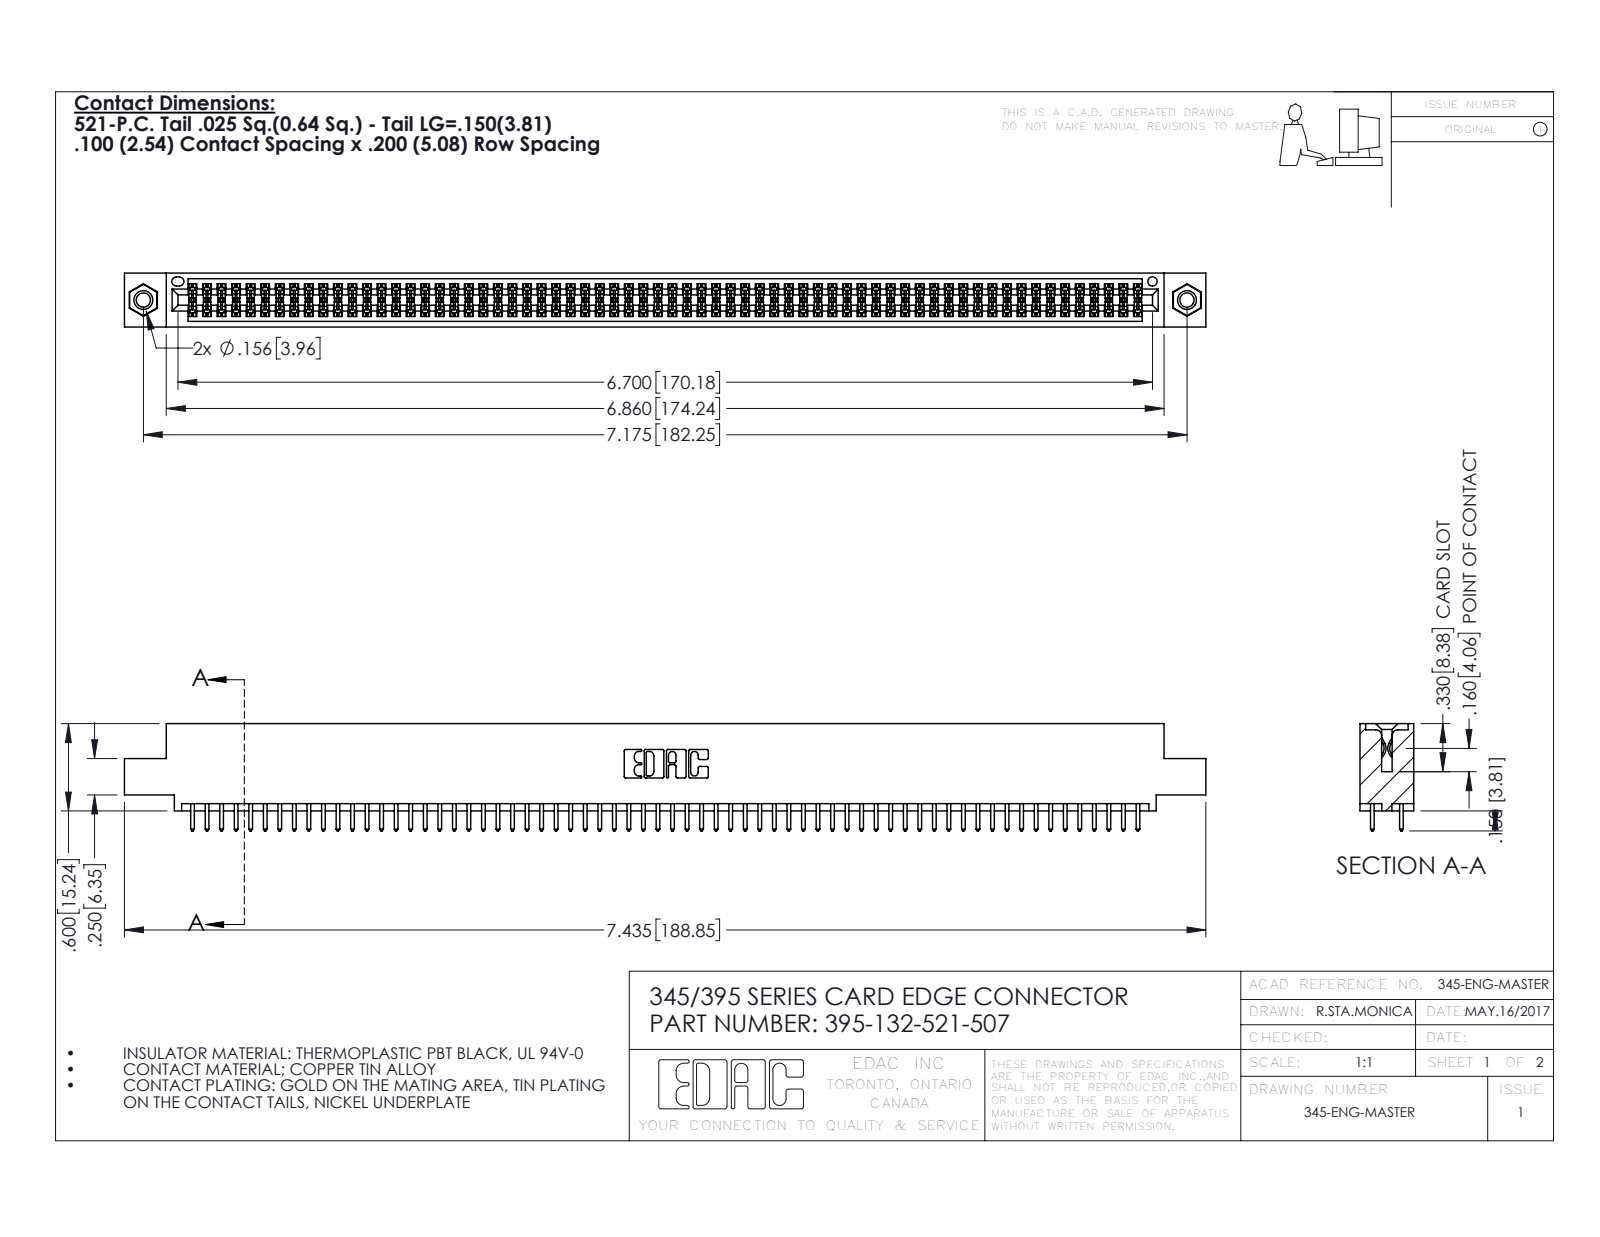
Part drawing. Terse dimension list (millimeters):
name: 345-292-001_345-293-121; 345-250-001_345-250-005-103; 345 Part_0.110 Offset - 0.156 Dia-TI; 395-132-521-507
written by: SolidWorks 2016 (CONFIG_CONTROL_DESIGN)
unit: mm
bodies: 135 solids, 6790 faces (4472 planar, 2302 cylindrical, 16 other)
size: 188.8 × 18.7 × 9.4
volume: 18 420 mm³; area: 27 470 mm²
holes: 2× ⌀2.5, 2× ⌀3.2, 2× ⌀4, 1× ⌀1.6
bosses: 2× ⌀3.9
rounds: 198× R0.2, 132× R0.3, 22× R0.3, 6× R0.2, 6× R0.8, 3× R0.7, 2× R0.4, 2× R0.5
face distances: 1.8, 7.6, 5.1, 2.5, 6.9, 0.6, 9.4, 5.7, 4.4, 3.8
hole spacings: 6.9, 176.3, 182.2
